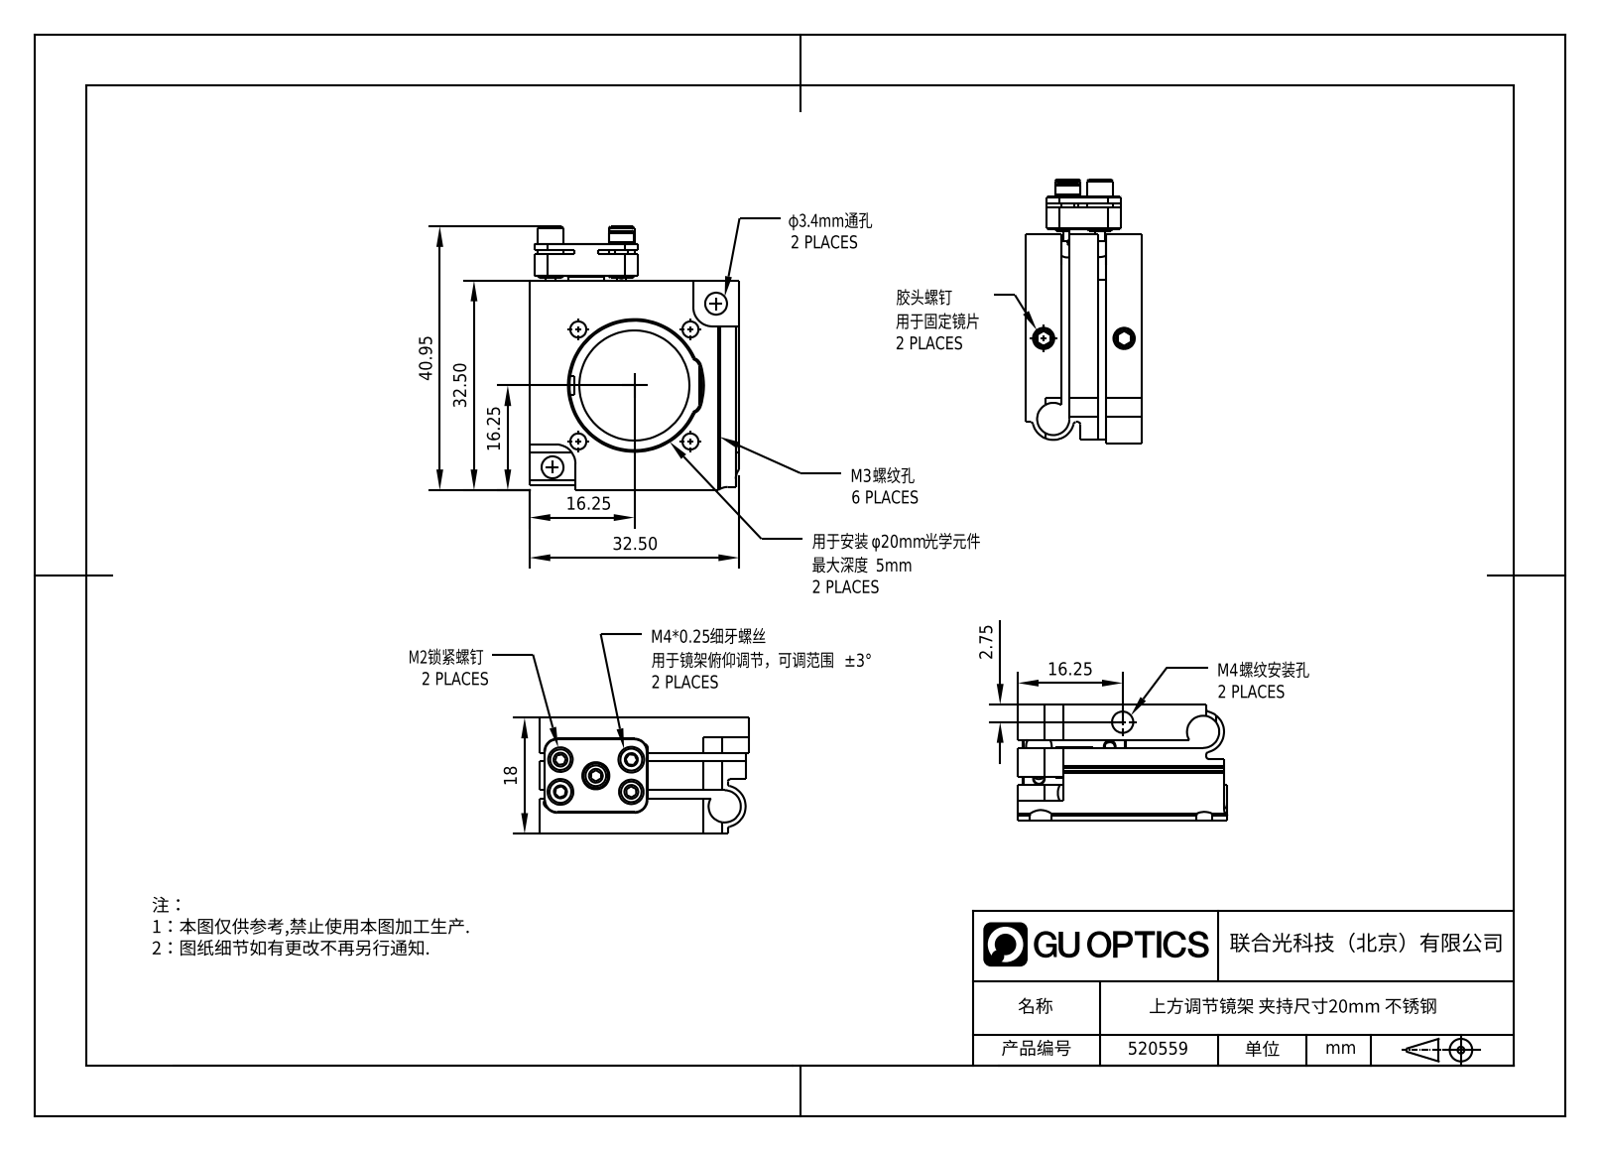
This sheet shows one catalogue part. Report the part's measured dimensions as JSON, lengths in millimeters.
{"part_name": "1.1.6.47_ZJR-BS20", "step_written_by": "SolidWorks 2021 (CONFIG_CONTROL_DESIGN)", "units": "millimeters", "bodies": {"solids": 0, "faces": 309, "planar": 124, "cylindrical": 115, "other": 70}, "overall_size": [40.95, 32.5, 18], "round_holes": [[2.5, 6], [3.3, 3], [3.4, 2], [5, 2], [1.5, 1], [4, 1], [17.1, 1], [20.1, 1]], "round_bosses_or_shafts": [[1.5, 5], [4, 2], [3.8, 2], [3, 2]], "partial_cylinders_radius": [[0.35, 6], [2, 6], [1.5, 4], [0.5, 2], [2.25, 2], [2.5, 2], [3, 2], [3.25, 2]], "face_to_face_distances": [5.75, 11.25, 6.75, 1.25, 12.5, 5.5, 4.5, 7, 18, 0.5], "hole_center_spacings": [21.77, 5.66, 12.3, 17.4, 17.96, 25.4, 30.26, 12.59]}
